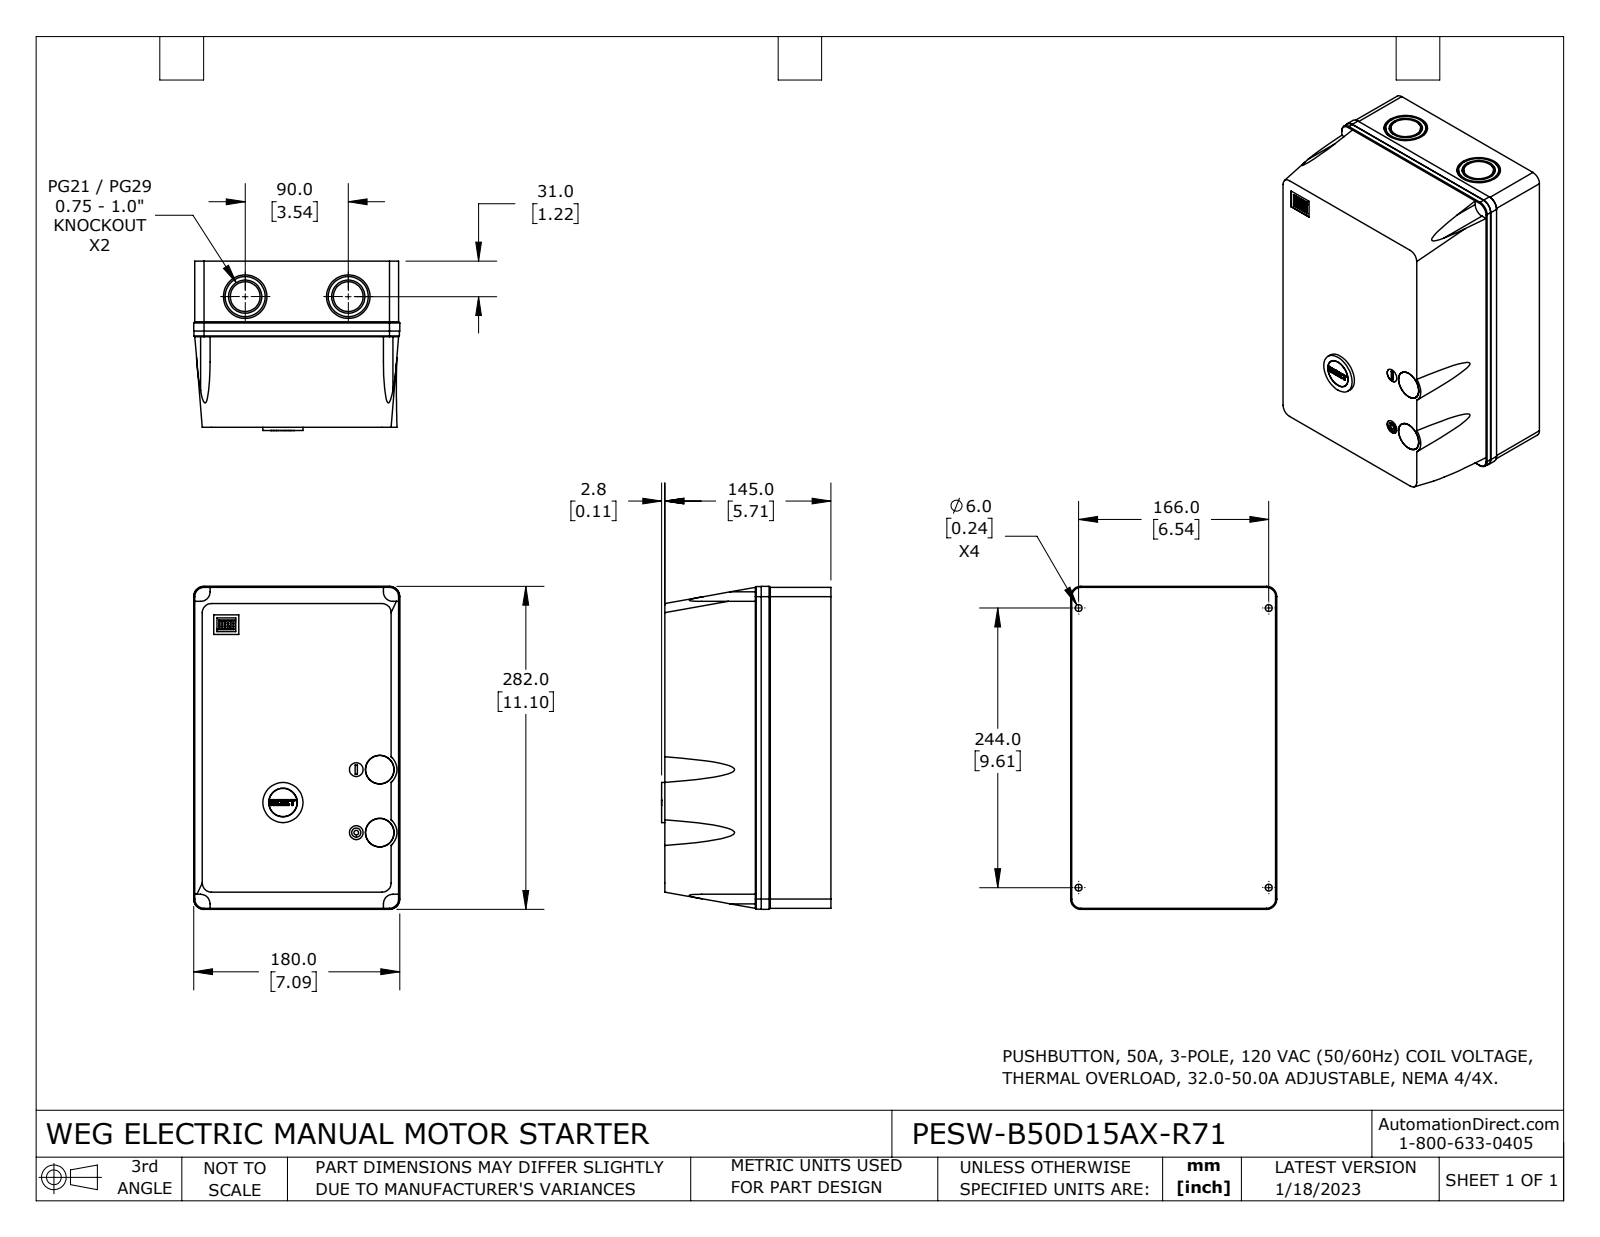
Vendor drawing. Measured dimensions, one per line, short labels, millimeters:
name: PESW-B50D15AX-R71
written by: SolidWorks 2021 (CONFIG_CONTROL_DESIGN)
unit: mm
bodies: 3 solids, 286 faces (130 planar, 144 cylindrical, 12 other)
size: 282 × 180 × 147.9
volume: 7 014 000 mm³; area: 232 257 mm²
holes: 4× ⌀6, 3× ⌀25, 2× ⌀12, 2× ⌀29, 2× ⌀38, 1× ⌀4, 1× ⌀30.5
bosses: 3× ⌀35, 2× ⌀26, 2× ⌀24.8, 1× ⌀30.3, 1× ⌀24.6, 1× ⌀14, 1× ⌀8
rounds: 34× R0.1, 4× R8, 4× R8.3, 4× R8.7, 4× R9, 1× R1.6
face distances: 145, 178, 280, 1, 0.7, 179, 179.7, 178.7, 281, 180
hole spacings: 20.5, 55, 58.7, 166, 244, 295.11, 49.14, 57.14
